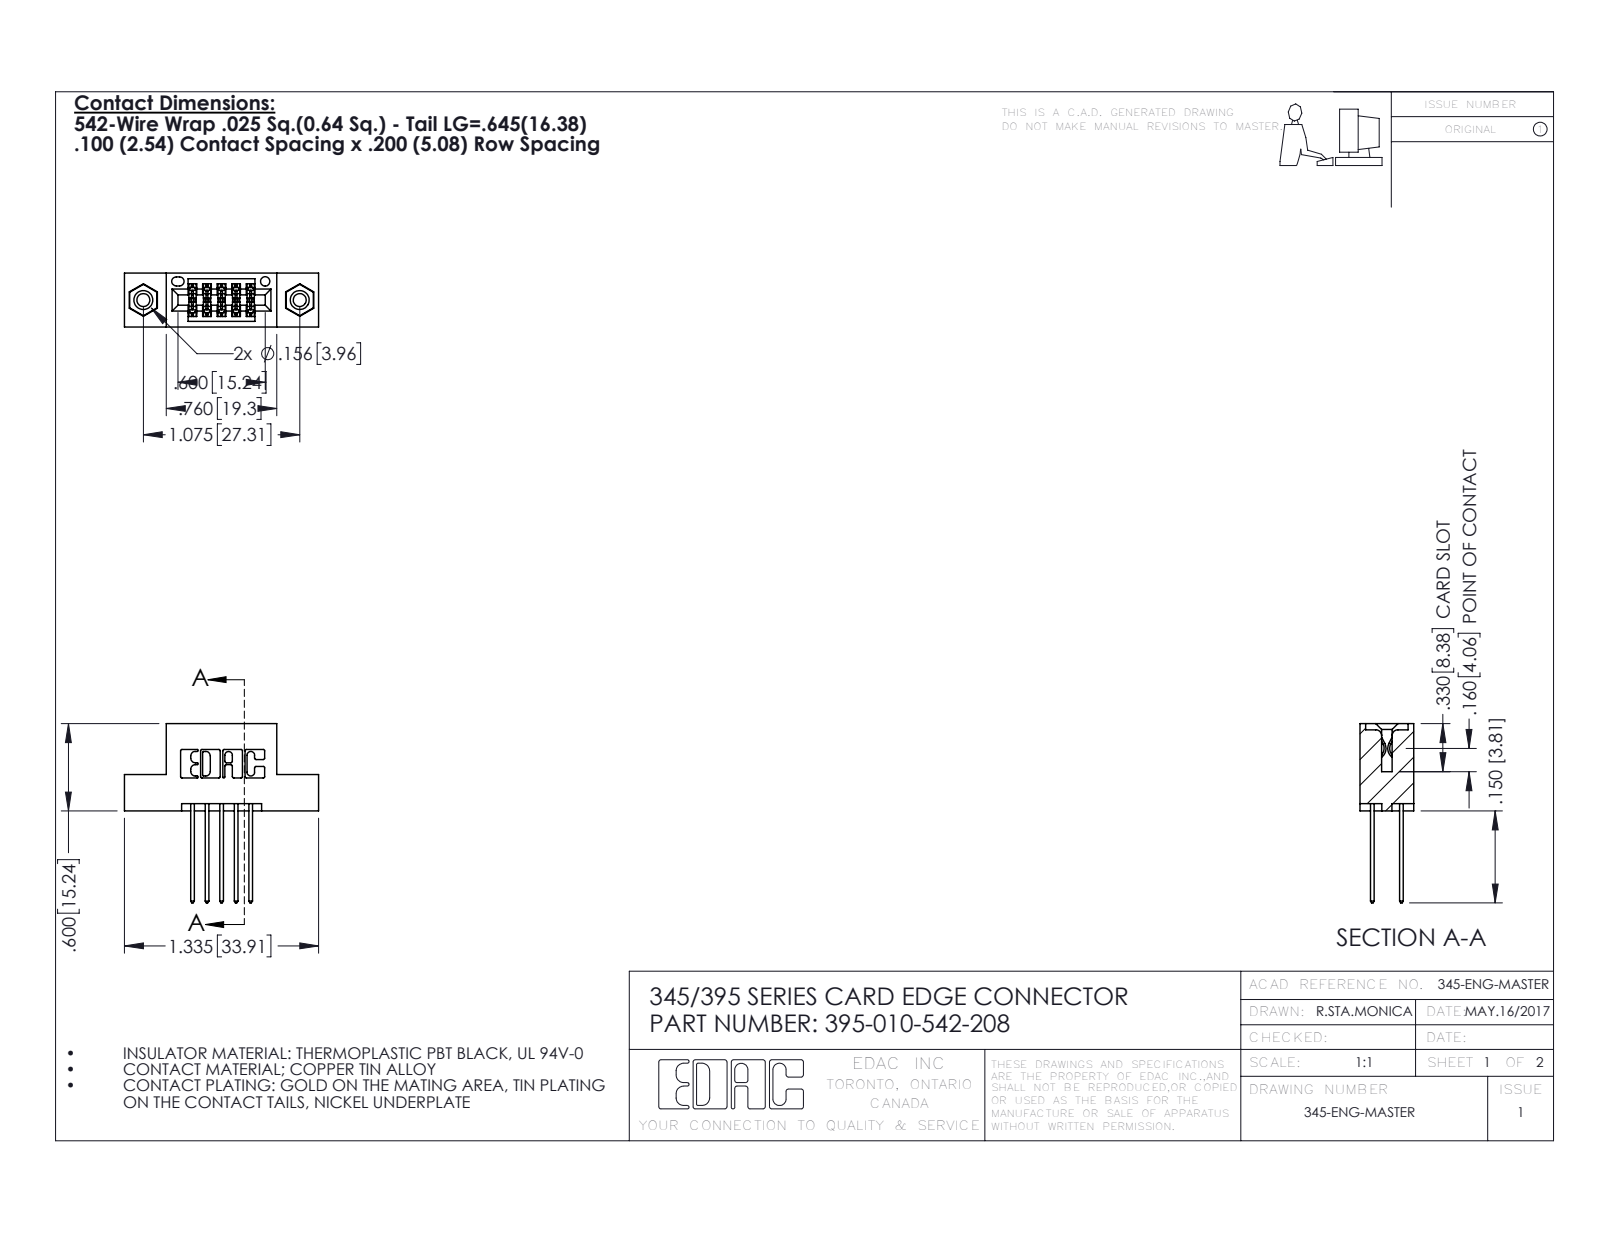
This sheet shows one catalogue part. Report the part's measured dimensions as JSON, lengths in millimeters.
{"part_name": "395-010-542-208; 345 Part_Flush Mounting Lugs - 0.156 Dia-TI; 345-292-001_345-293-142; 345-250-001_345-250-003-102", "step_written_by": "SolidWorks 2016 (CONFIG_CONTROL_DESIGN)", "units": "millimeters", "bodies": {"solids": 13, "faces": 686, "planar": 442, "cylindrical": 228, "other": 16}, "overall_size": [33.9, 31.3, 9.4], "volume_mm3": 2980, "surface_area_mm2": 3935, "round_holes": [[2.3, 2], [3.2, 2], [4, 2], [1.6, 1]], "round_bosses_or_shafts": [[3.9, 2]], "partial_cylinders_radius": [[0.3, 22], [0.2, 15], [0.3, 10], [0.2, 6], [0.8, 6], [0.7, 3], [0.4, 2], [0.5, 2]], "face_to_face_distances": [5.1, 1.8, 7.6, 2.5, 9.4, 2.5, 6.9, 0.6, 5.7, 8.9], "hole_center_spacings": [6.9, 21.5, 27.3]}
